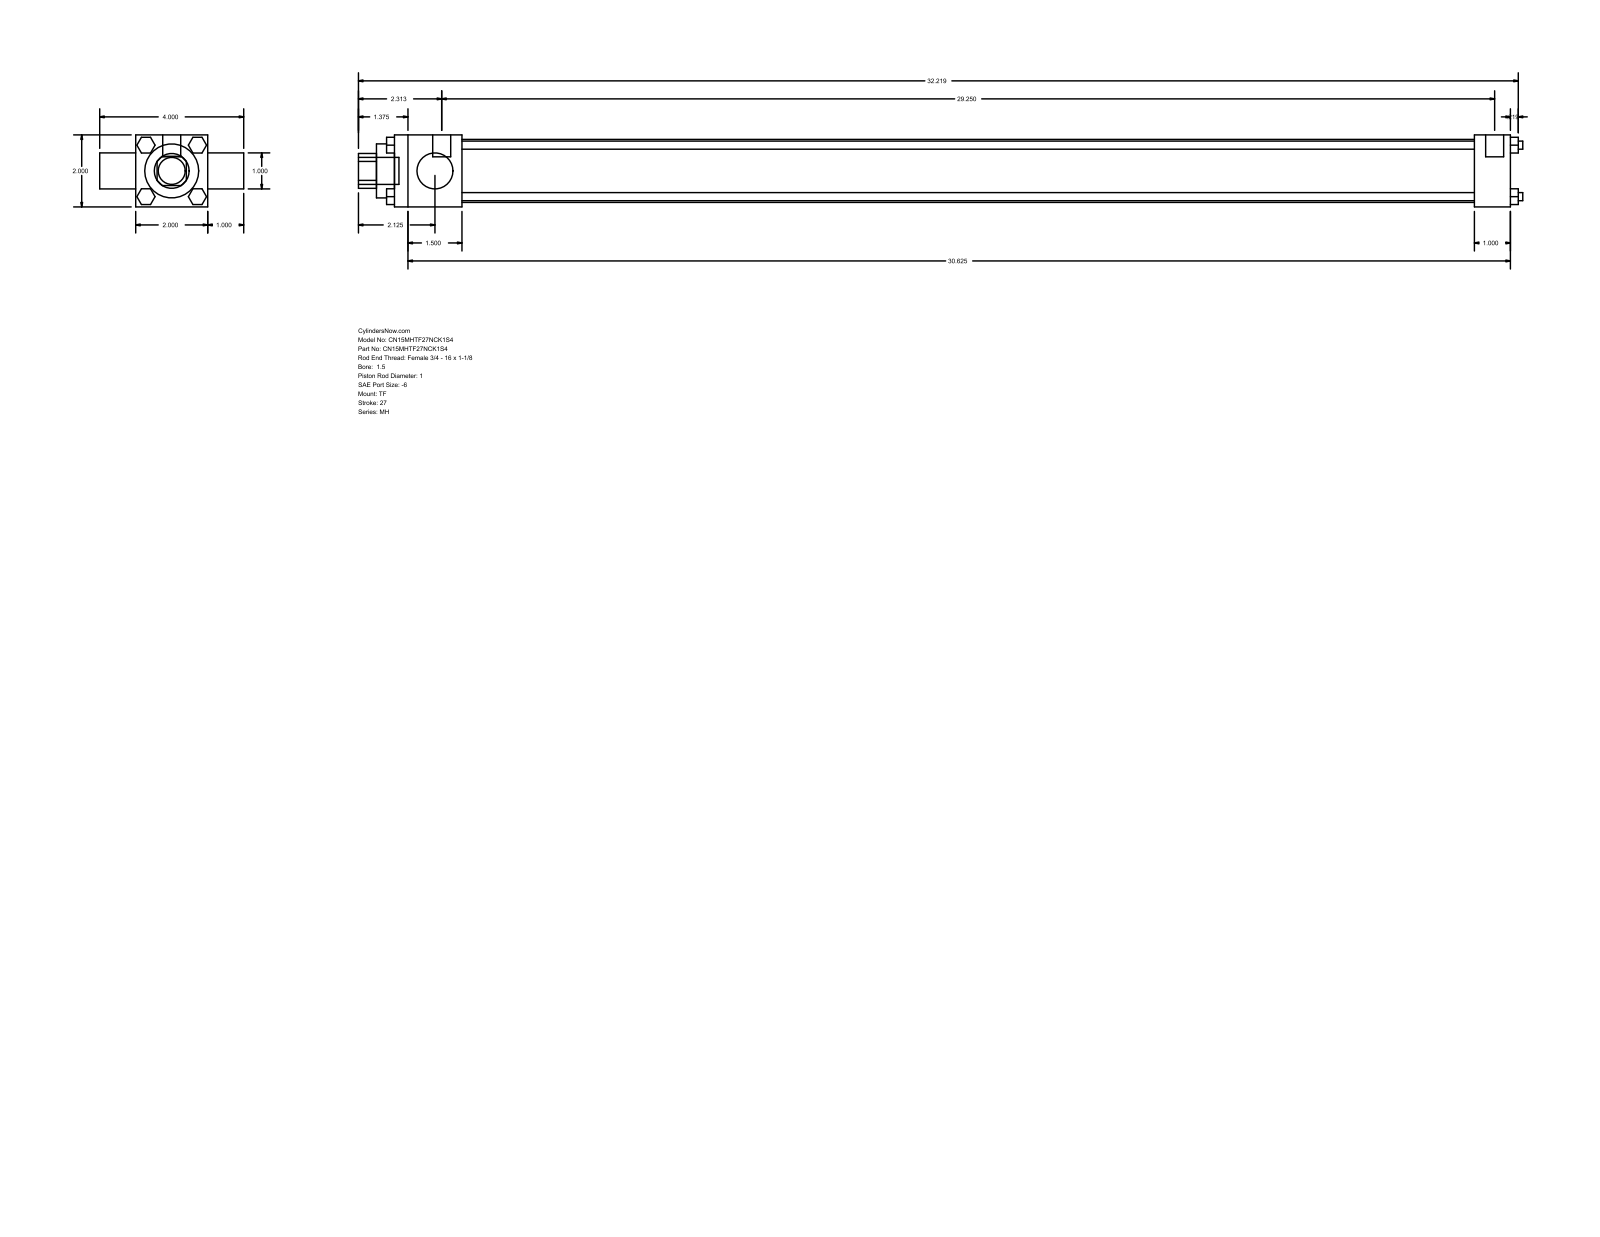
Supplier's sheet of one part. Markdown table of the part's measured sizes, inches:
| quantity | value |
| --- | --- |
| part name | MH_TF__0150_1 |
| STEP written by | GSSL Pune (CONFIG_CONTROL_DESIGN) |
| units | inches |
| bodies | 0 solids, 120 faces (92 planar, 28 cylindrical, 0 other) |
| overall size | 32.344 × 4 × 2 |
| round holes (diameter × count) | 1 × 2, 1.5 × 1, 1.75 × 1 |
| round bosses / shafts (diameter × count) | 0.225 × 4, 0.219 × 3, 0.5 × 2, 0.75 × 1 |
| partial cylindrical surfaces (radius × count) | 0.484 × 1 |
| main face-to-face distances | 2, 1, 31, 3, 1.875, 29.125, 30, 28.125, 31.219, 0.5 |
